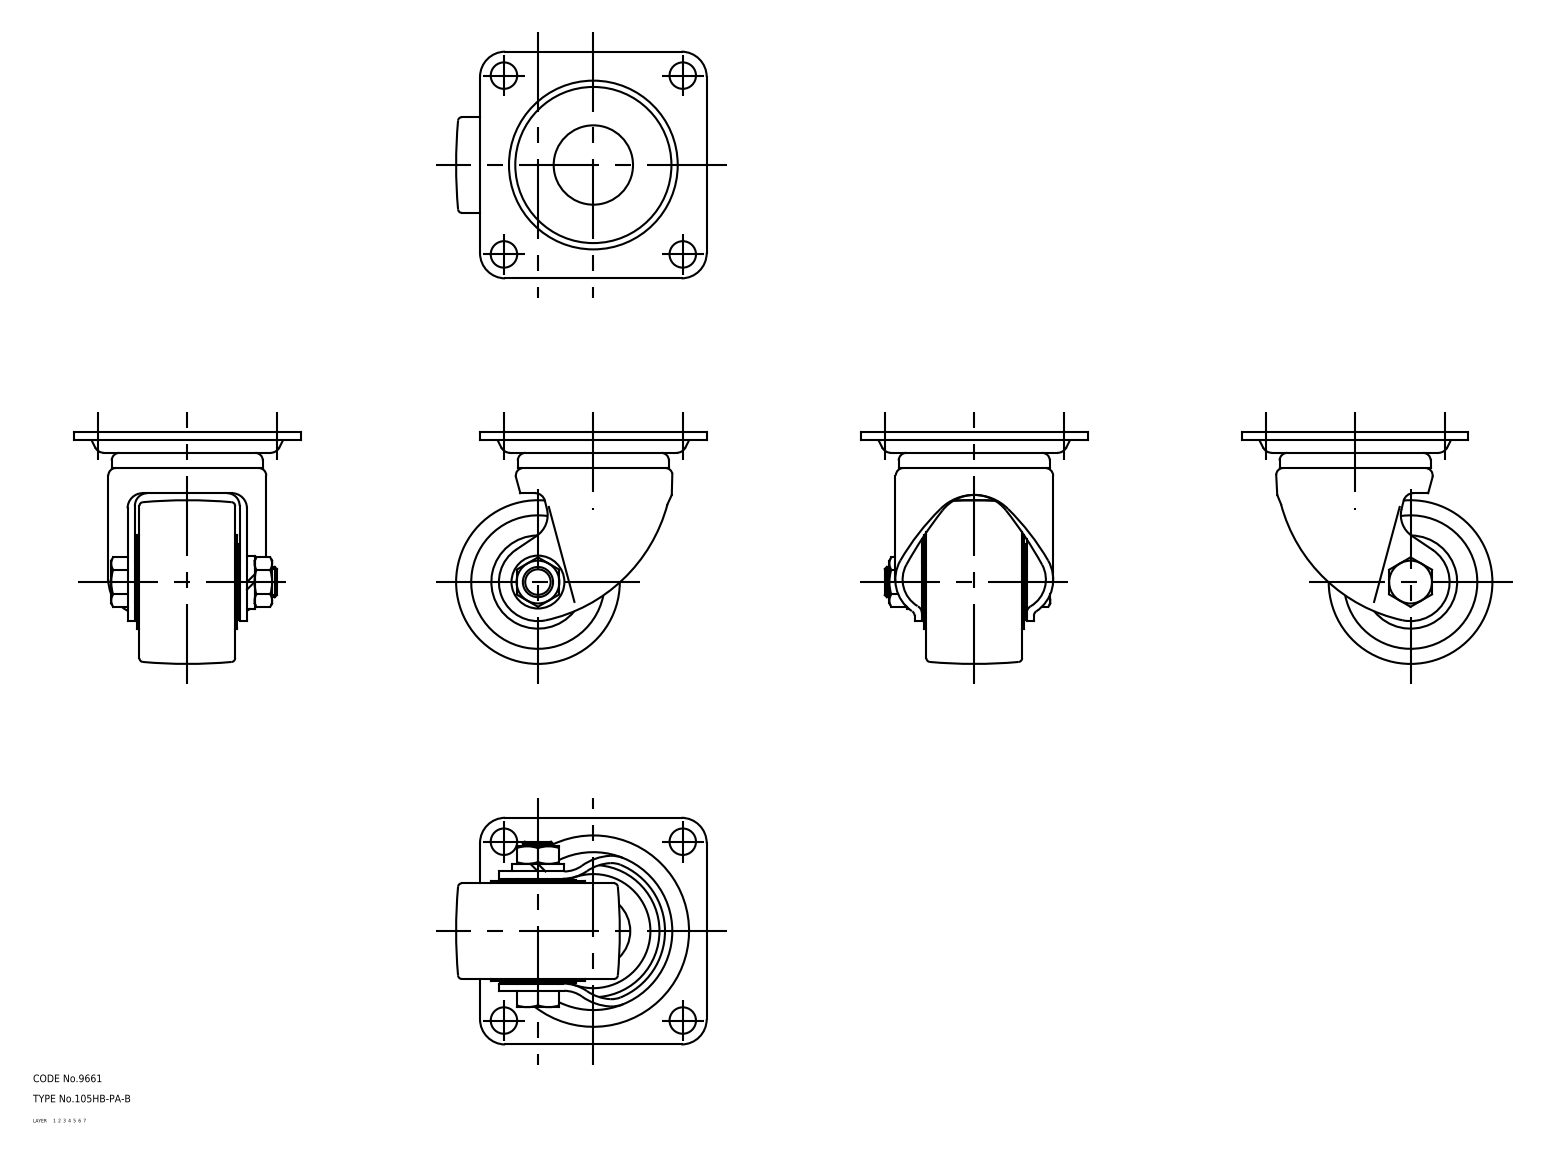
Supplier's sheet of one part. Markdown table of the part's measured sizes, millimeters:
| quantity | value |
| --- | --- |
| part name | 67125946; 67125959; 67125972; 67125985 (+1 more) |
| STEP written by | CADfix (AUTOMOTIVE_DESIGN) |
| units | millimeters |
| bodies | 5 solids, 253 faces (0 planar, 0 cylindrical, 253 other) |
| overall size | 99.5 × 92 × 90 |
| volume | 226 490 mm³ |
| surface area | 62 195 mm² |
